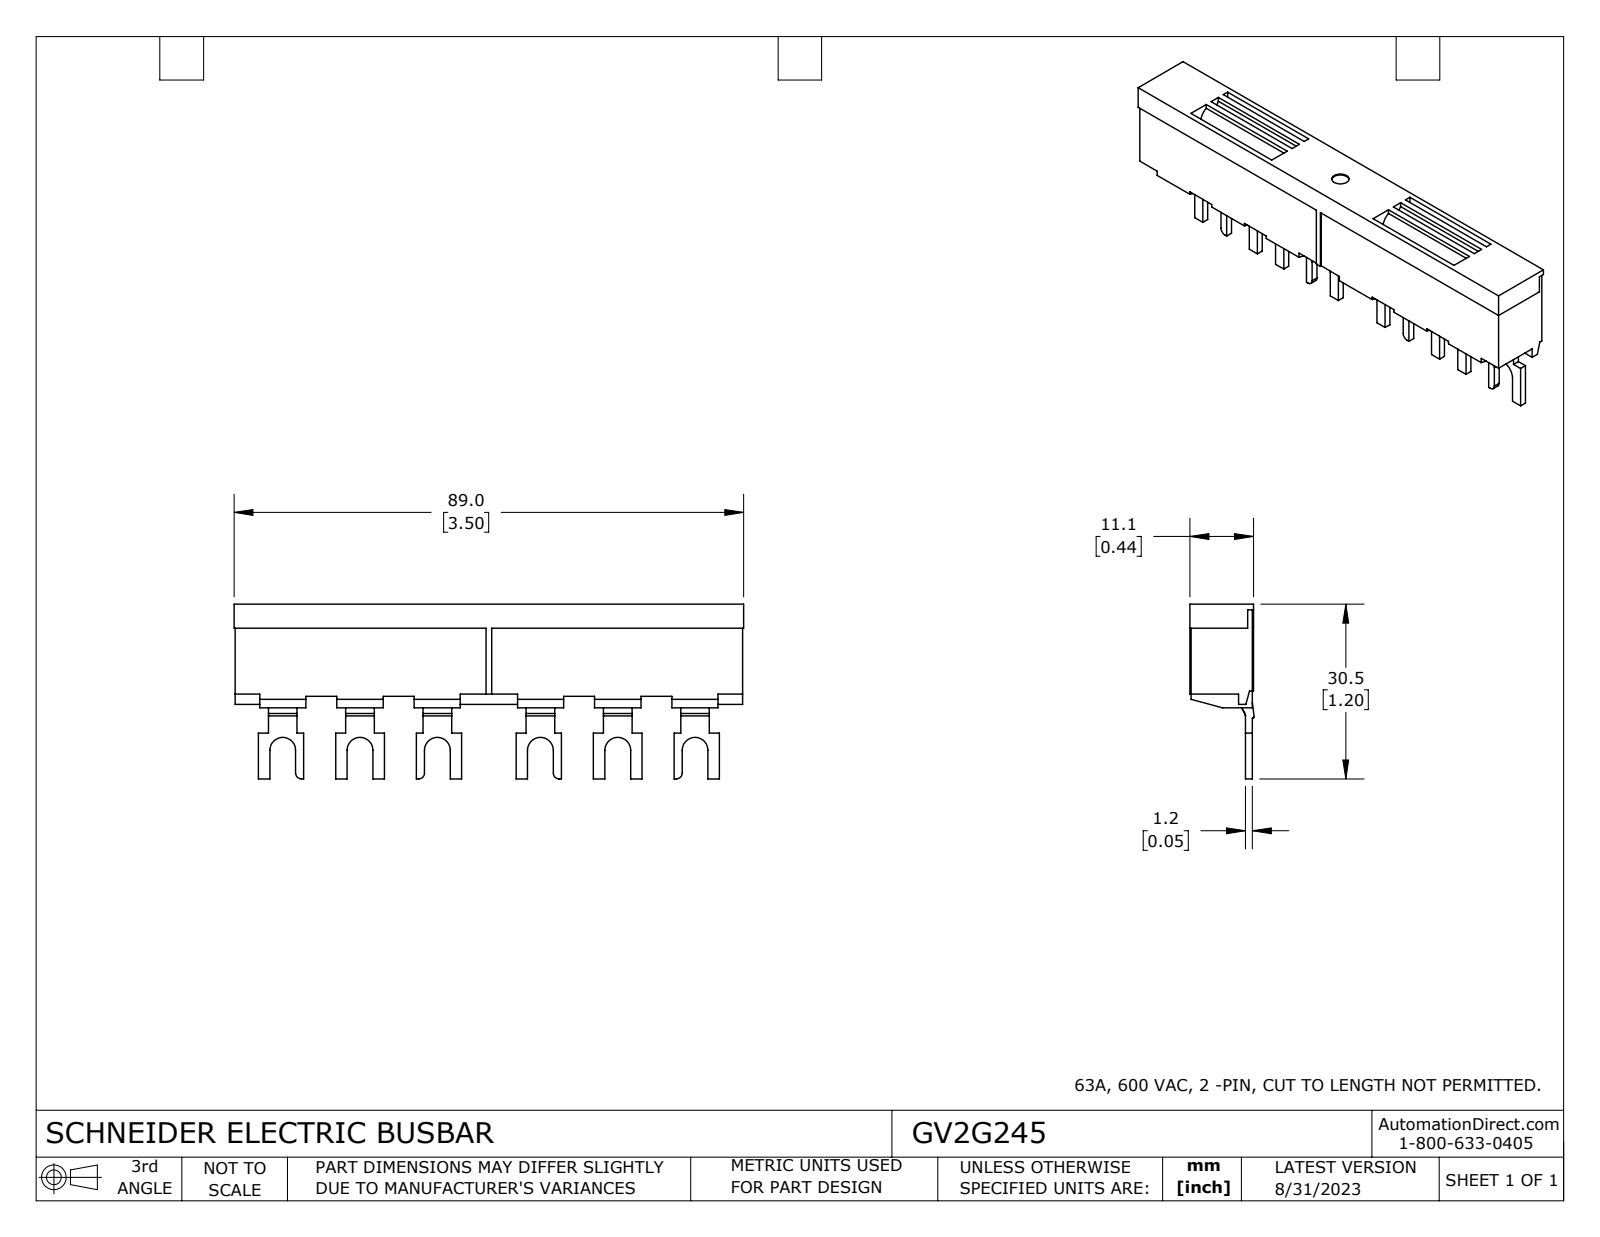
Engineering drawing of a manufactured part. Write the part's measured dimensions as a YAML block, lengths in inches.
part_name: "GV2G245"
step_written_by: "SolidWorks 2021 (CONFIG_CONTROL_DESIGN)"
units: inches
bodies: {solids: 1, faces: 229, planar: 209, cylindrical: 20, other: 0}
overall_size: [3.504, 1.201, 0.442]
volume: 0.981
surface_area: 11.19
round_holes:
  - {diameter: 0.118, count: 1}
partial_cylinders:
  - {radius: 0.089, count: 6}
  - {radius: 0.039, count: 4}
  - {radius: 0.031, count: 1}
  - {radius: 0.098, count: 1}
face_to_face_distances: [0.421, 0.429, 0.047, 0.374, 0.382, 0.031, 0.039, 0.634, 0.079, 0.39]
